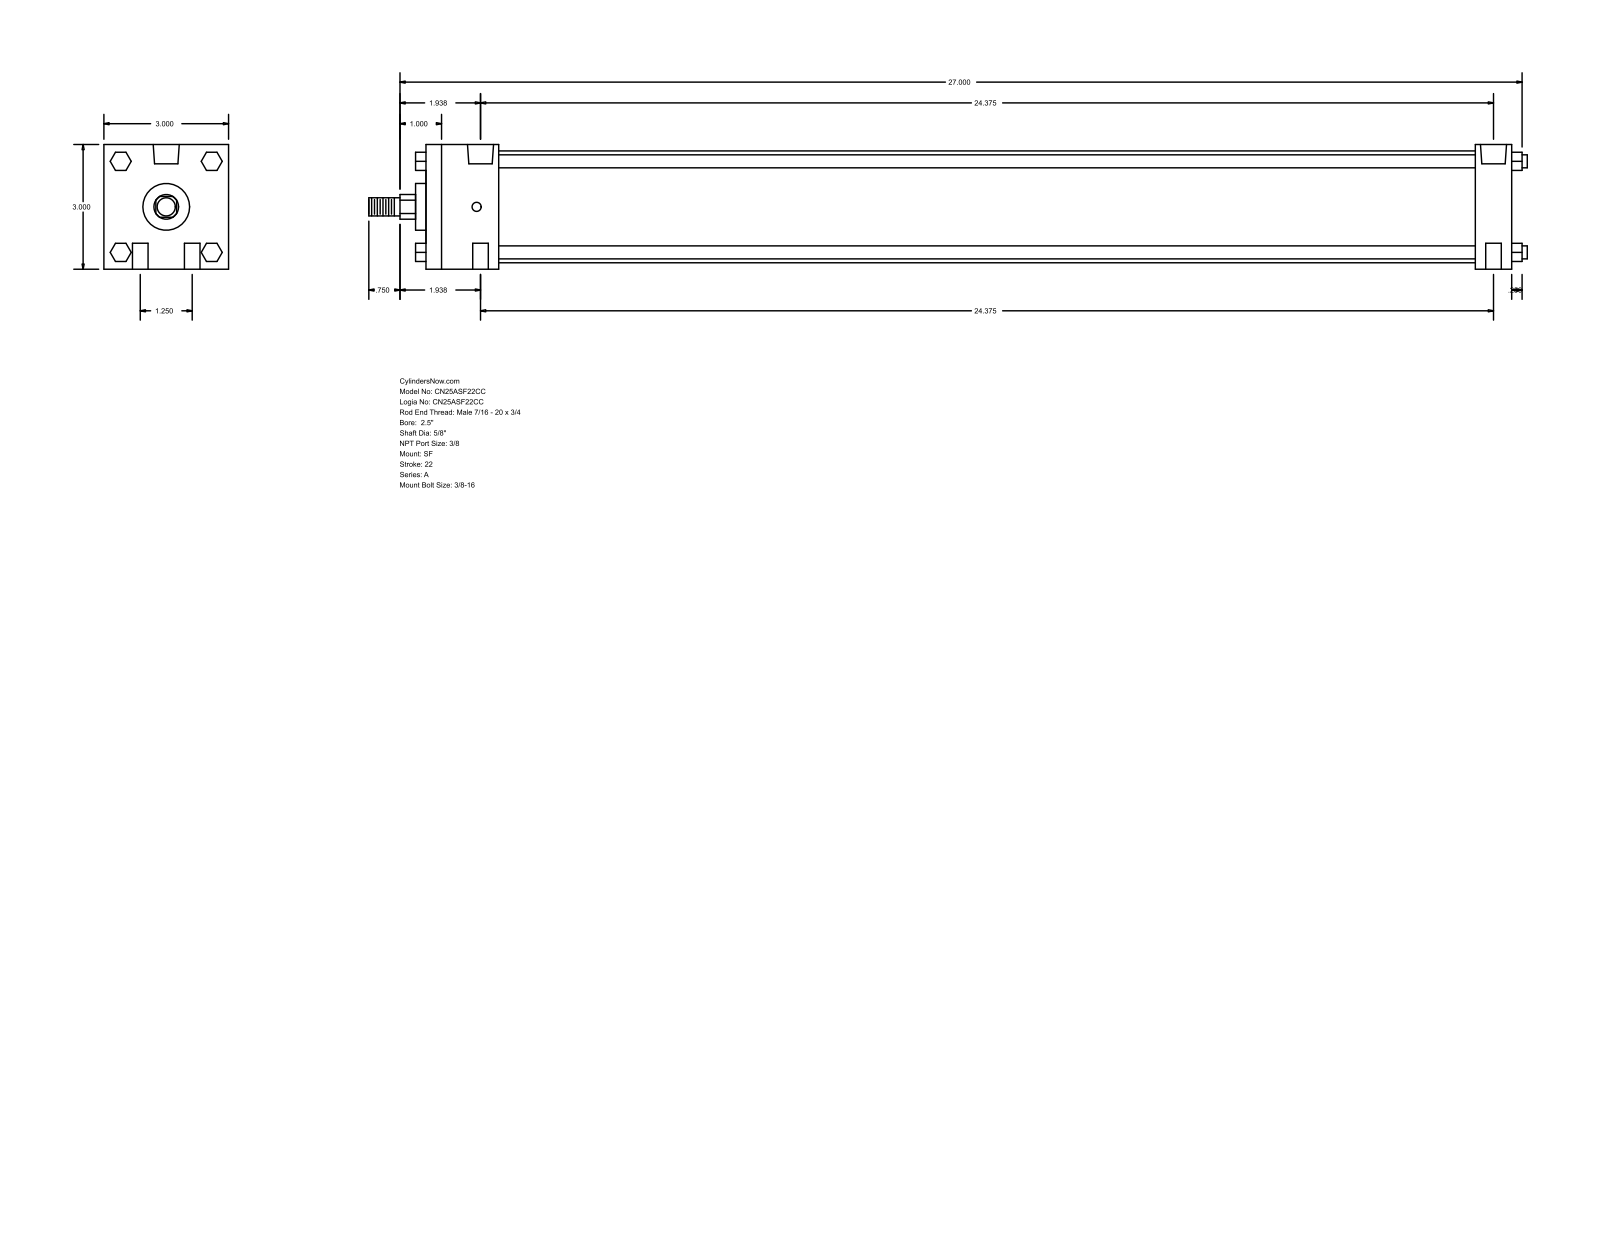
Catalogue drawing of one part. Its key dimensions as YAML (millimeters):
part_name: "A_SF__0250_0.625"
step_written_by: "GSSL Pune (CONFIG_CONTROL_DESIGN)"
units: millimeters
bodies: {solids: 0, faces: 124, planar: 94, cylindrical: 30, other: 0}
overall_size: [708.02, 76.2, 76.2]
round_holes:
  - {diameter: 9.53, count: 4}
  - {diameter: 5.56, count: 2}
  - {diameter: 15.93, count: 2}
round_bosses_or_shafts:
  - {diameter: 7.94, count: 4}
  - {diameter: 68.33, count: 1}
  - {diameter: 28.57, count: 1}
  - {diameter: 15.88, count: 1}
  - {diameter: 11.11, count: 1}
partial_cylinders:
  - {radius: 7.54, count: 1}
face_to_face_distances: [76.2, 663.57, 44.45, 641.35, 22.22, 596.9, 619.12, 6.35, 669.92, 50.8]
hole_center_spacings: [15.88, 619.33, 619.13, 31.76, 619.94, 623.89]
